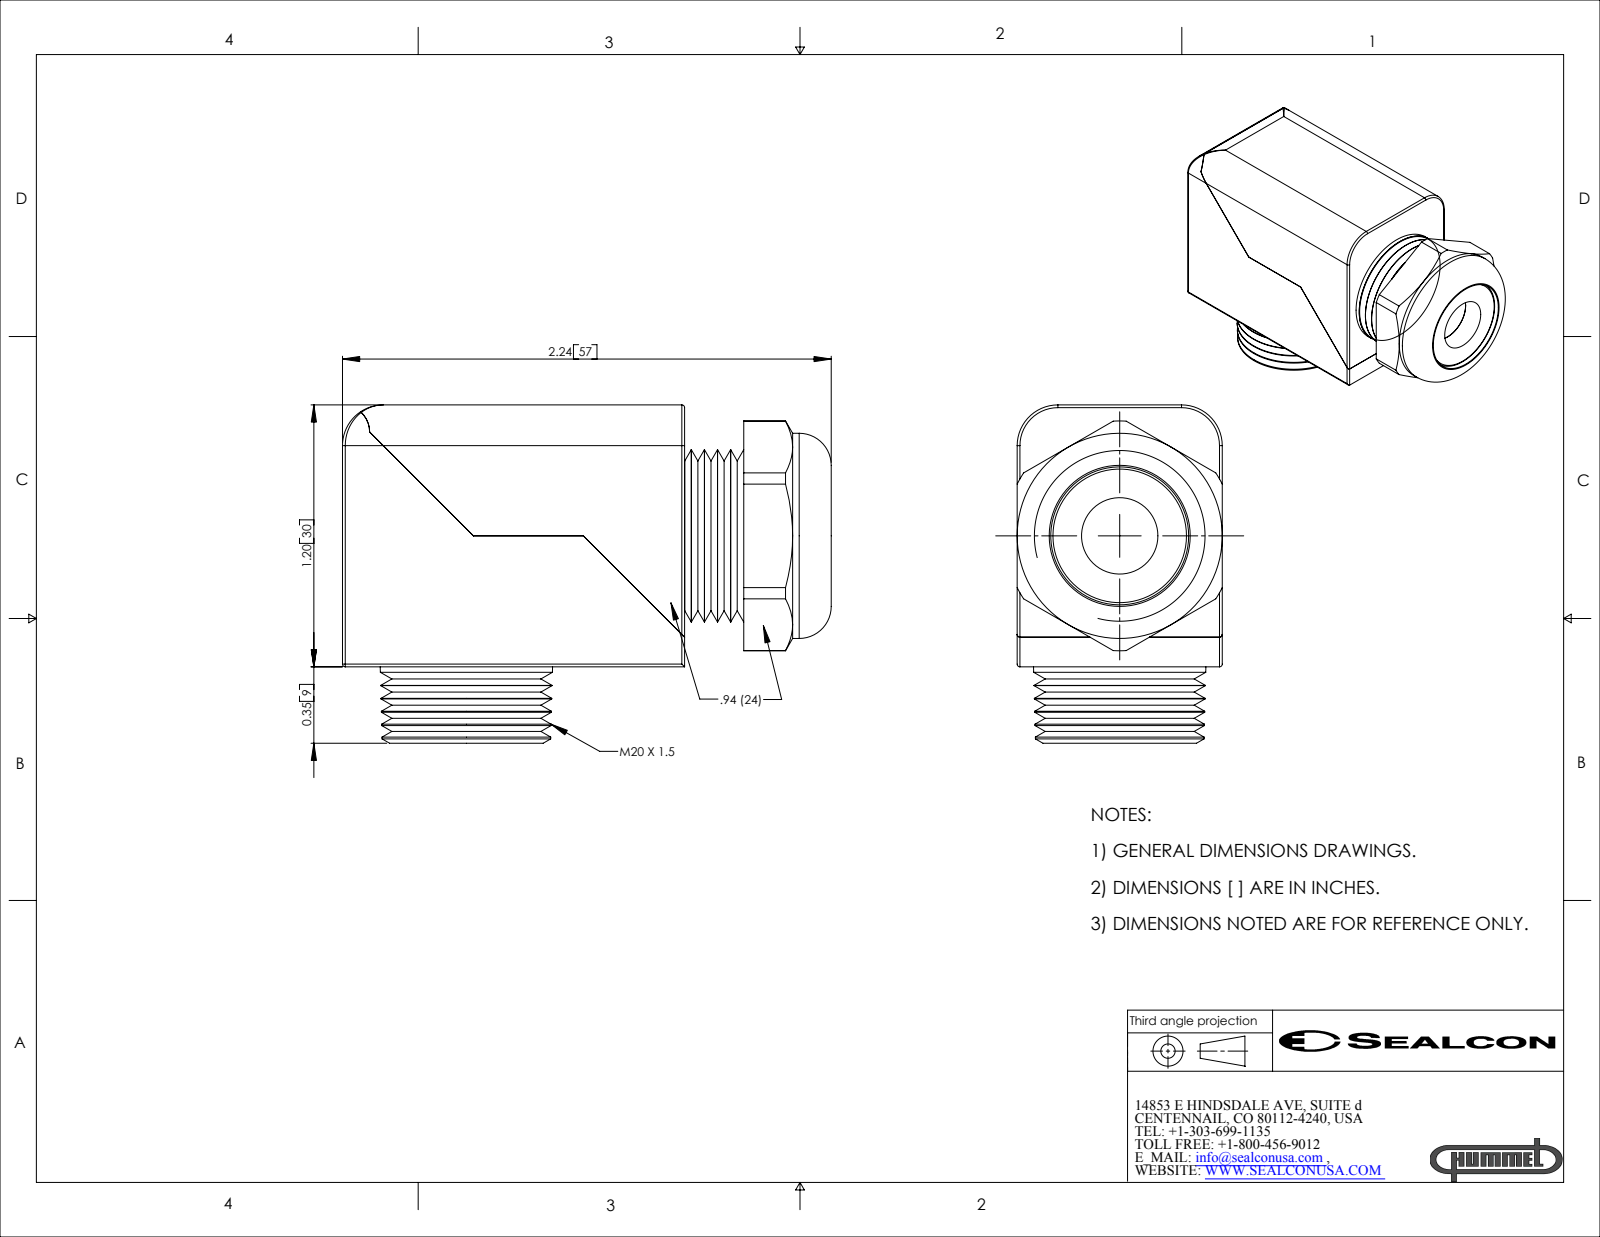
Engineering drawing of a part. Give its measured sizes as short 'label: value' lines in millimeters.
name: ED20MR-GY
written by: SolidWorks 2007 (CONFIG_CONTROL_DESIGN)
unit: mm
bodies: 3 solids, 151 faces (29 planar, 48 cylindrical, 74 other)
size: 56.9 × 39.4 × 23.9
volume: 33 130 mm³; area: 12 720 mm²
holes: 2× ⌀8.9, 1× ⌀16.1
bosses: 1× ⌀23.9, 1× ⌀20.1
rounds: 8× R0.3, 3× R4.7, 1× R3.1, 1× R13.4
face distances: 23.9, 15.2, 9, 30.5, 39.8, 12.6, 52.4, 5.7, 6.9, 46.7
